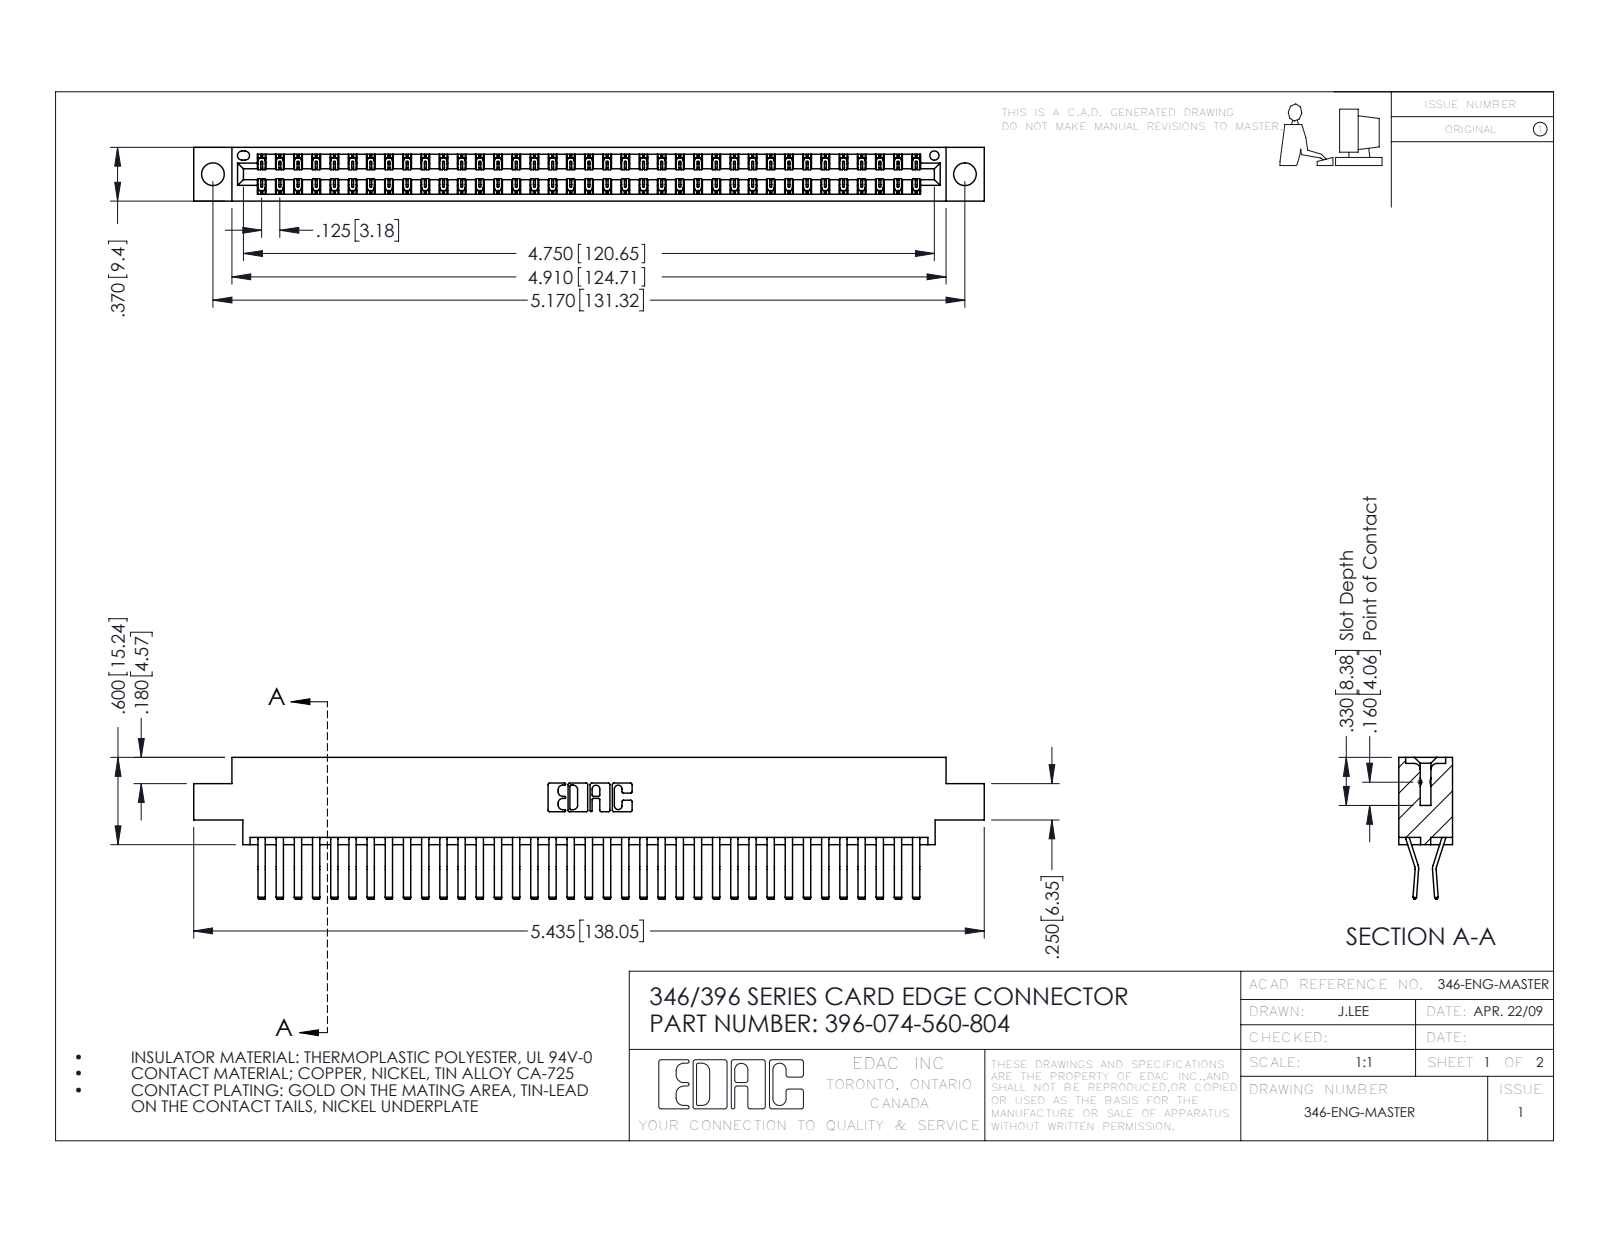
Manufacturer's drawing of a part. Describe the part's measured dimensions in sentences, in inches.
The part is named "346 Part_0.170 Offset - 0.156 Dia-TH; 345-292-001_560 Tail; 396-074-560-804". Its 3-D file was written by "SolidWorks 2016 (CONFIG_CONTROL_DESIGN)". It is 75 solids with 4122 faces: 2670 planar, 1452 cylindrical and 0 other. Overall it measures 5.435 by 0.975 by 0.37 inches. Its volume is 0.834 cubic inches and its surface area 30.99 square inches. Round holes: 2 of diameter 0.156, 1 of diameter 0.064. Partial cylindrical surfaces (rounded edges, fillets, slot ends): 111 of radius 0.006, 22 of radius 0.01, 6 of radius 0.007, 6 of radius 0.031, 3 of radius 0.026, 2 of radius 0.01, 2 of radius 0.014, 2 of radius 0.022. The main face-to-face distances are 0.048, 0.322, 0.37, 0.025, 0.25, 0.072, 0.298, 0.275, 0.148, 0.222. The hole center spacings are 0.246, 4.961, 5.17.
